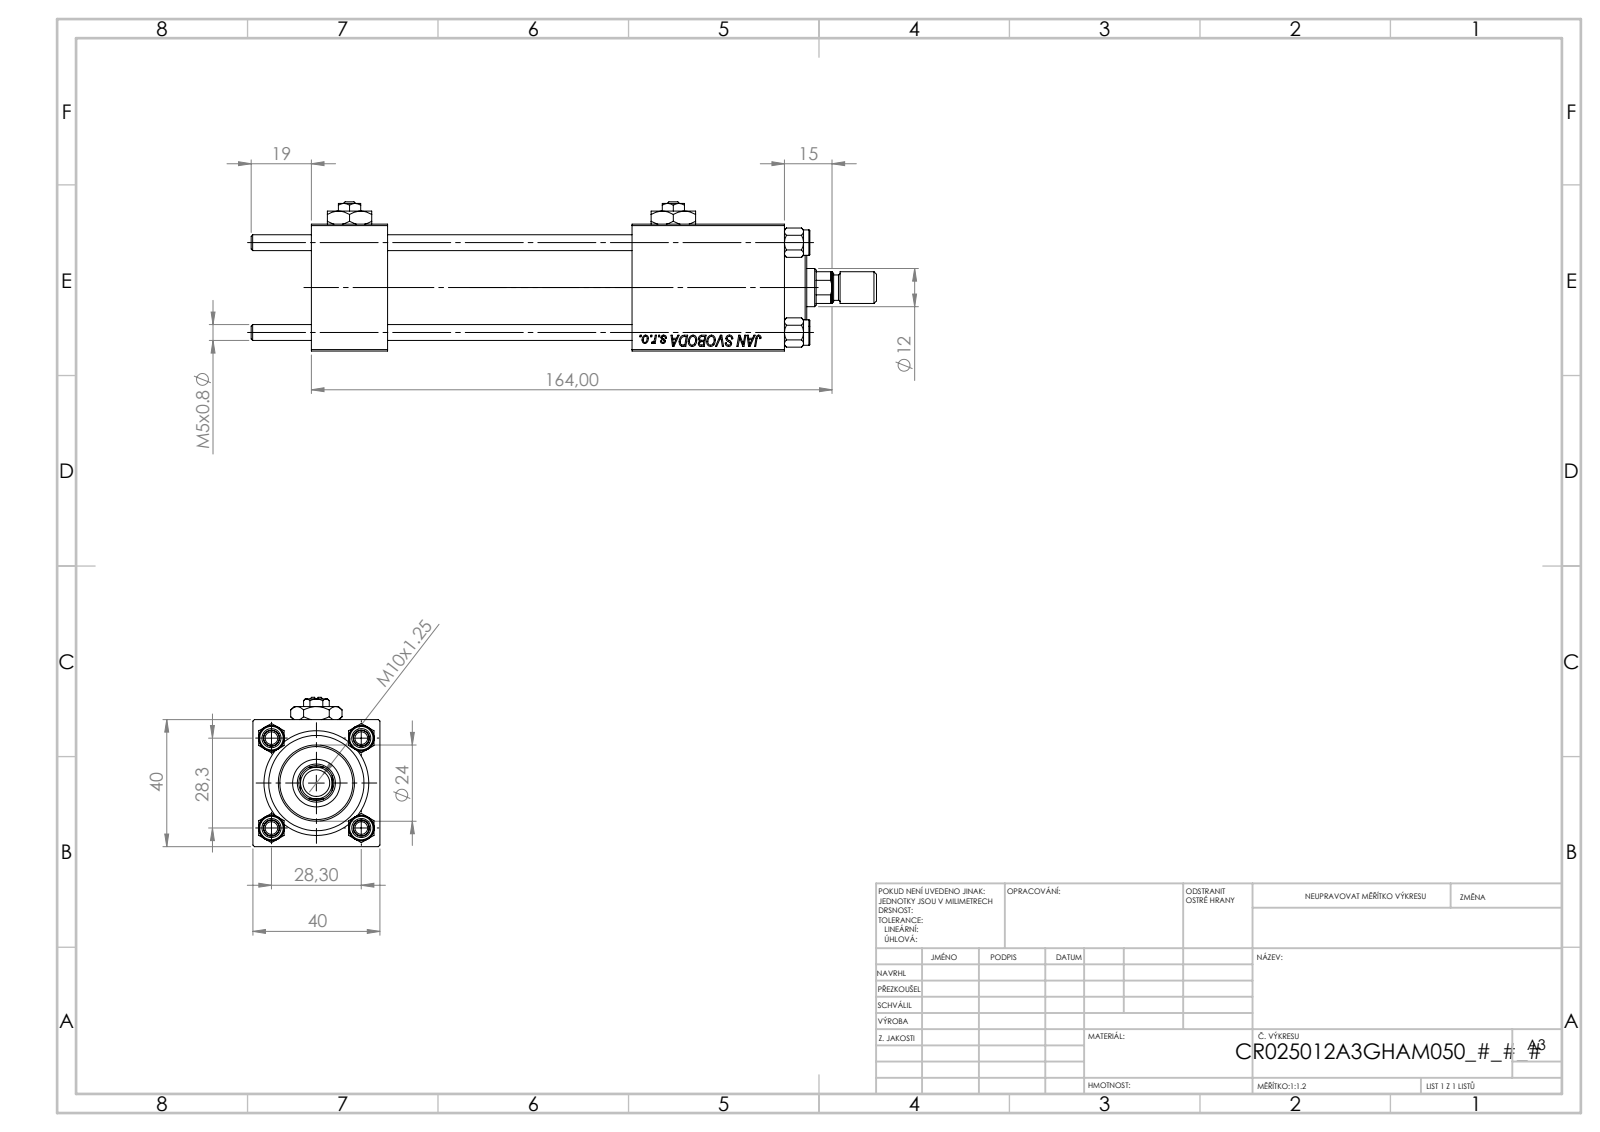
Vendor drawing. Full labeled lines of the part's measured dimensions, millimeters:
Part name (STEP PRODUCT): V215_VC_A; V215CR_VCP; CR025_012_A_0_G_A_G_M_020_+#_##_TYCINKA; V215CR_BODY_A (+3 more)
STEP written by: SolidWorks 2019 (CONFIG_CONTROL_DESIGN)
Units: millimetres
Bodies: 14 solids, 1246 faces (568 planar, 94 cylindrical, 584 other)
Overall size (bounding box): 197 × 47 × 40
Volume: 158 117 mm³ · Surface area: 69 543 mm²
Round holes (diameter × count): ⌀5 ×4, ⌀20 ×3, ⌀7 ×2, ⌀13.16 ×2, ⌀6.5 ×1, ⌀12 ×1, ⌀15 ×1, ⌀25 ×1, ⌀30 ×1
Round bosses / shafts (diameter × count): ⌀8 ×5, ⌀31 ×1, ⌀24 ×1, ⌀10 ×1
Partial cylindrical surfaces — rounded edges, fillets, slot ends (radius × count): R5.5 ×1
Main face-to-face distances: 40, 24, 39.8, 149, 125, 77, 120.3, 96.3, 28.7, 101
Hole centre spacings: 20.01, 28.3, 40.02, 102
